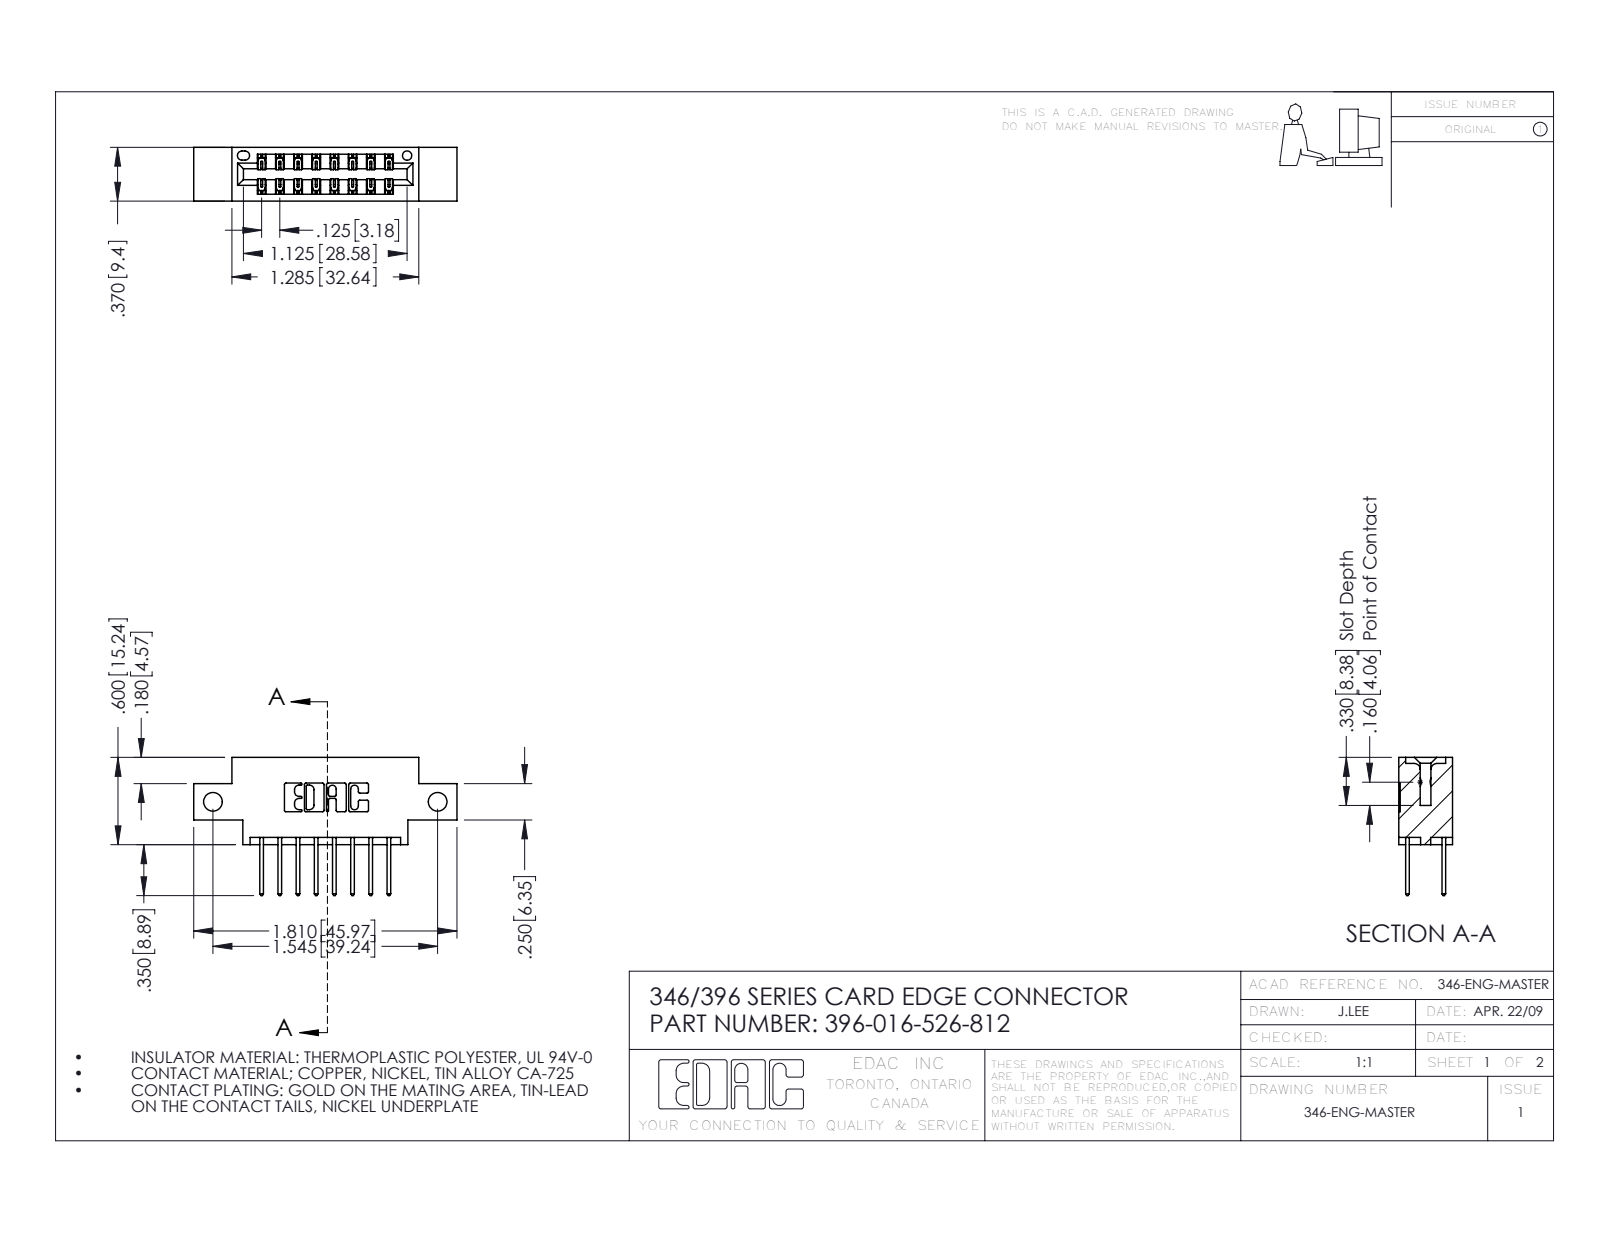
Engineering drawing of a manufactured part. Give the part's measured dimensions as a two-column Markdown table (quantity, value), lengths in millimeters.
| quantity | value |
| --- | --- |
| part name | 345-292-001_345-293-126; 396-016-526-812; 346 Part_0.170 Offset - Side Mount |
| STEP written by | SolidWorks 2016 (CONFIG_CONTROL_DESIGN) |
| units | millimeters |
| bodies | 17 solids, 958 faces (640 planar, 318 cylindrical, 0 other) |
| overall size | 46 × 24.1 × 9.4 |
| volume | 4 000 mm³ |
| surface area | 5 128 mm² |
| round holes (diameter × count) | 3.3 × 2, 1.6 × 1 |
| partial cylindrical surfaces (radius × count) | 0.2 × 24, 0.3 × 22, 0.3 × 16, 0.2 × 6, 0.8 × 6, 0.7 × 3, 0.4 × 2, 0.6 × 2 |
| main face-to-face distances | 6.4, 1.2, 8.2, 9.4, 1.8, 7.6, 0.6, 7, 3.8, 5.6 |
| hole center spacings | 39.2 |
